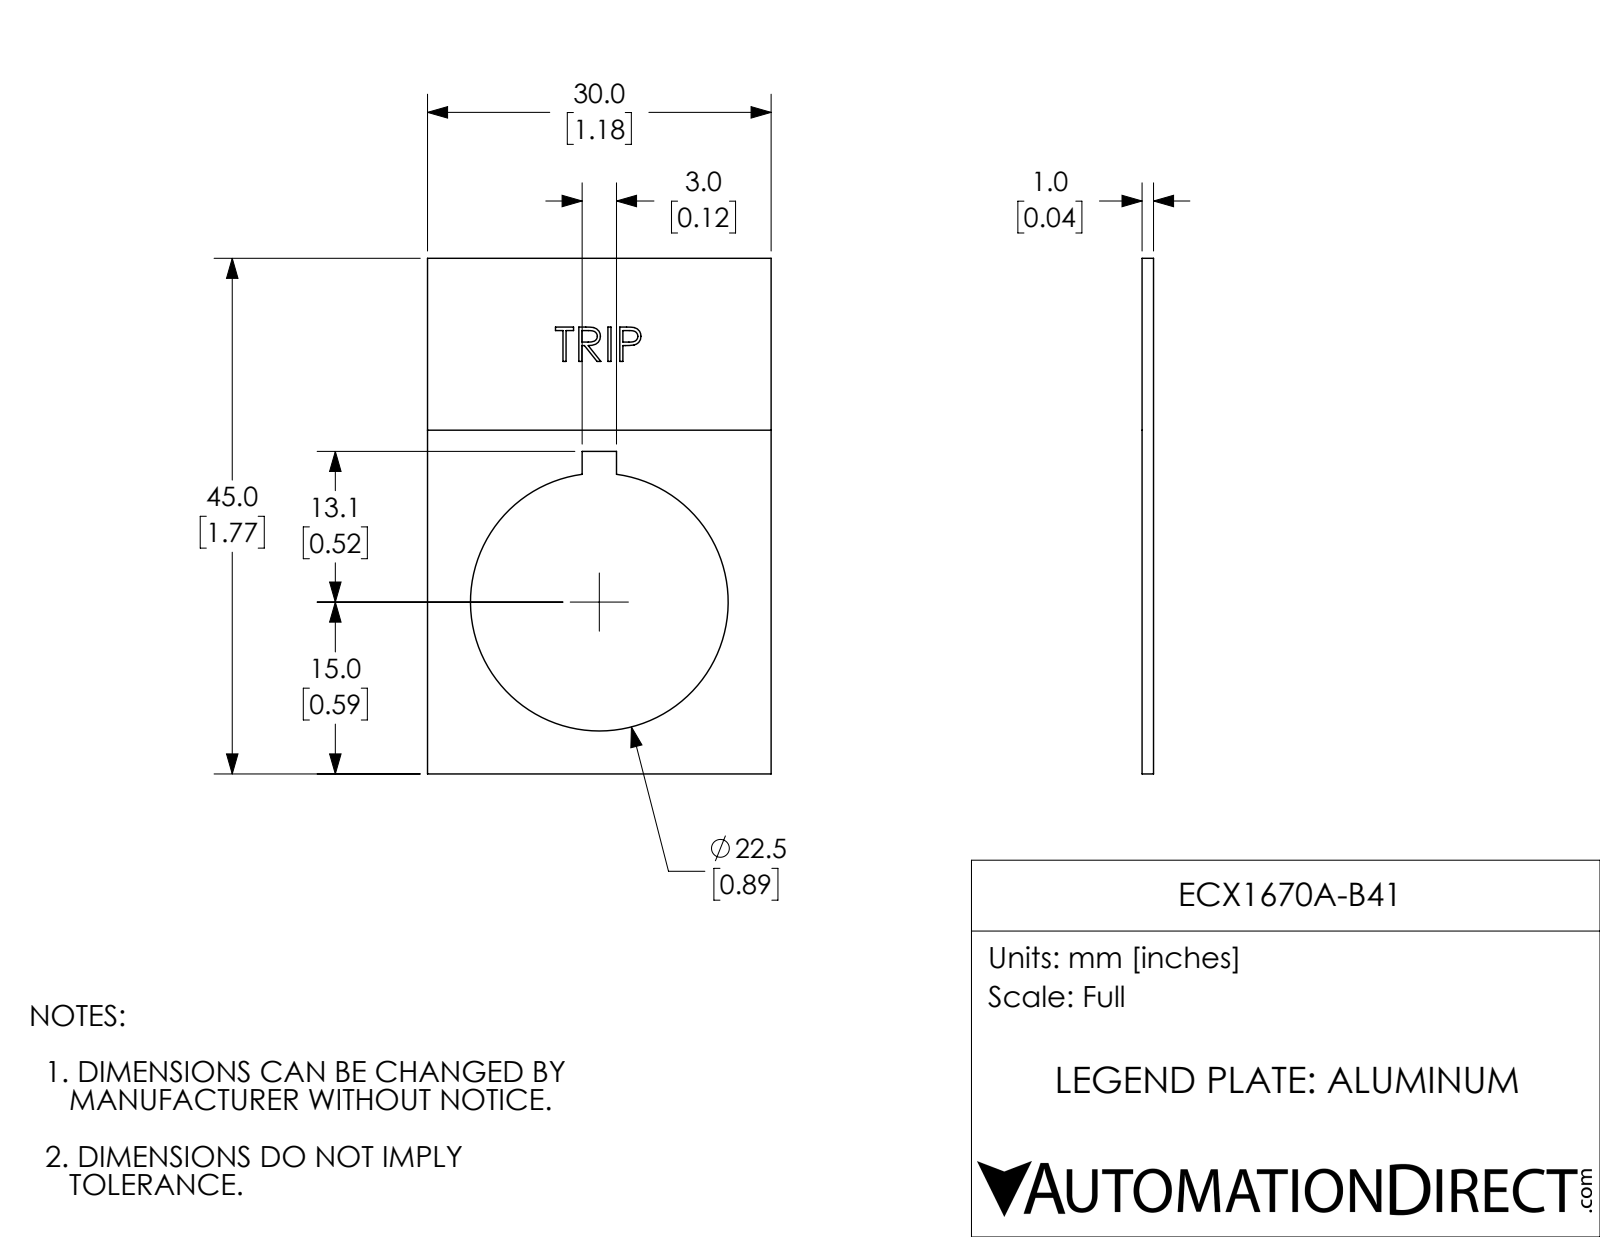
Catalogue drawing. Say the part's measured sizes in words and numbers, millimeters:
The part is named "ECX1670A-B41". Its 3-D file was written by "SolidWorks 2017 (AUTOMOTIVE_DESIGN)". It is 1 solid with 61 faces: 47 planar, 3 cylindrical and 11 other. Overall it measures 45 by 30 by 1 millimeters. Its volume is 950 cubic millimeters and its surface area 2 119 square millimeters. Round holes: 1 of diameter 22.5. The main face-to-face distances are 1, 30, 45, 1, 13.5, 16.5, 28.1, 16.8, 3, 13.2.
